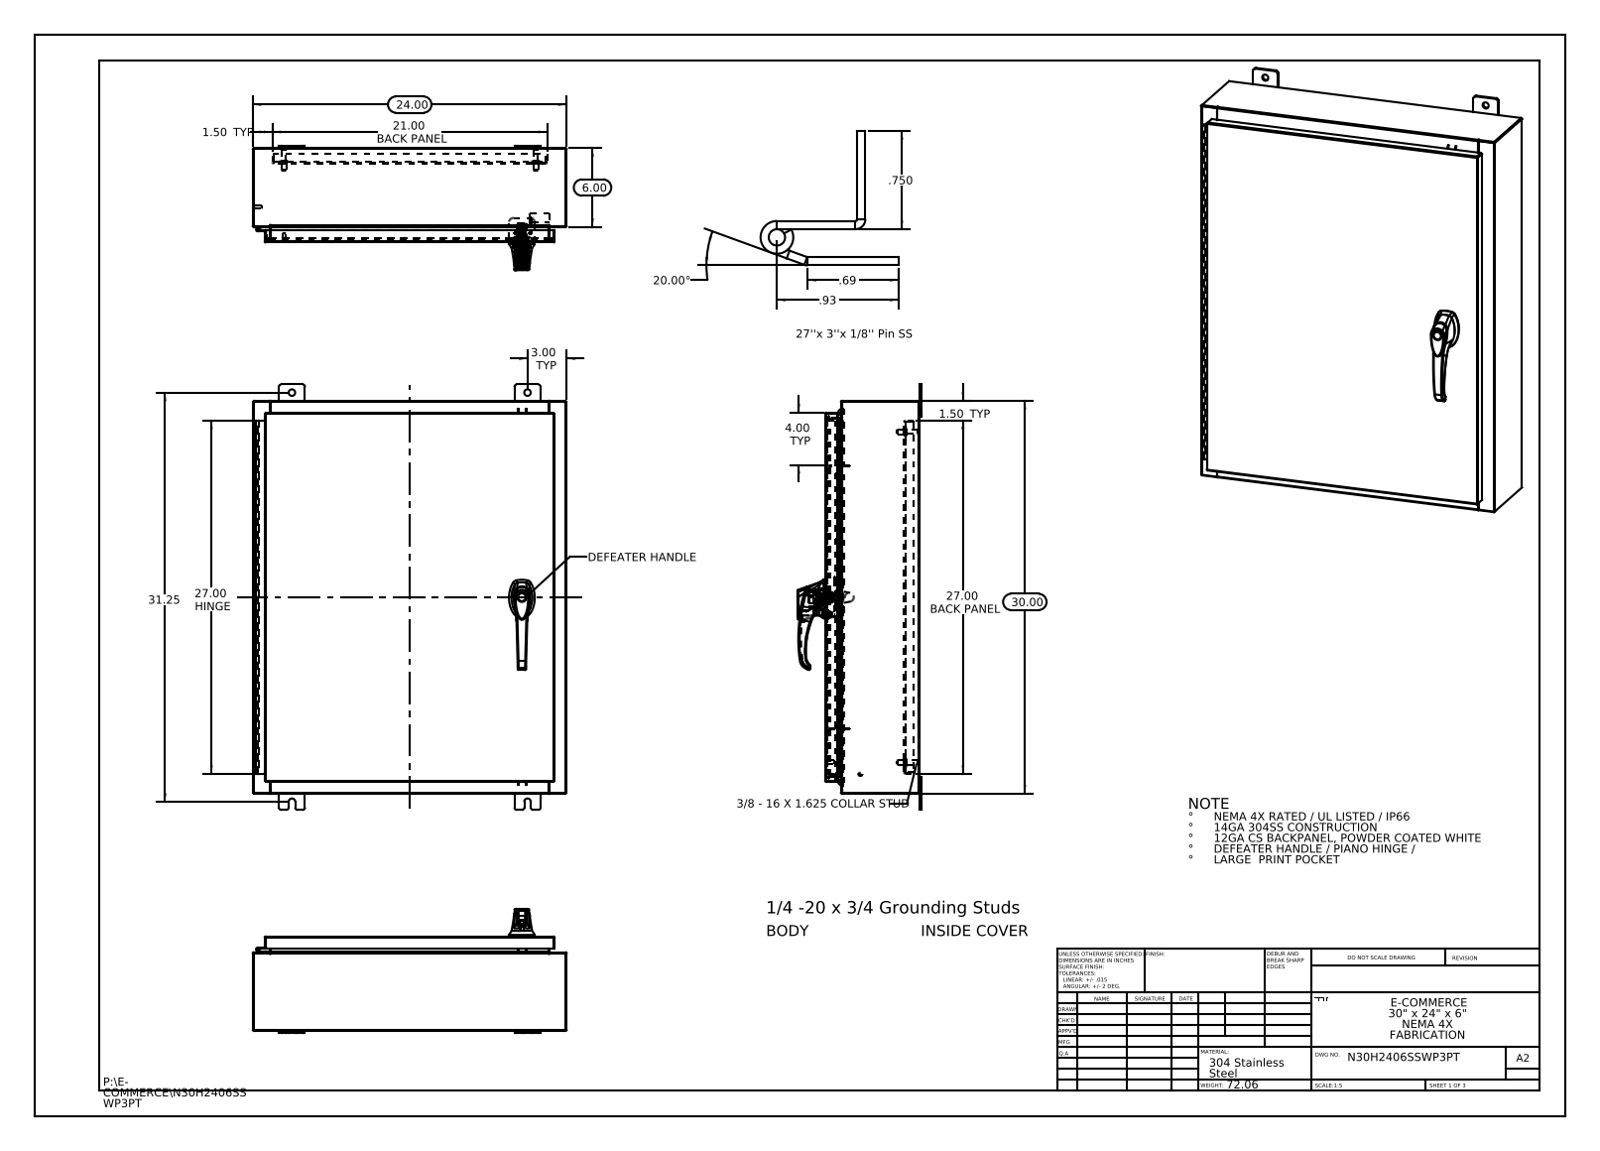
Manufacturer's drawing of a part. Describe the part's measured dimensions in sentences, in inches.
The part is named "297025; N30H2406SSWP3PT Hinge Cover Side; N30H2406SSWP3PT Mounting Studs; N30H2406SSWP3PT (+8 more)". Its 3-D file was written by "SolidWorks 2013 (CONFIG_CONTROL_DESIGN)". It is 37 solids with 2662 faces: 971 planar, 993 cylindrical and 698 other. Overall it measures 32.5 by 24 by 9.495 inches. Its volume is 256.1 cubic inches and its surface area 6 284 square inches. Round holes: 8 of diameter 0.5, 4 of diameter 0.25, 3 of diameter 0.138, 3 of diameter 0.161, 2 of diameter 0.079, 2 of diameter 0.203, 2 of diameter 0.313, 2 of diameter 0.437, 1 of diameter 0.125, 1 of diameter 0.125, 1 of diameter 0.197, 1 of diameter 0.276. Round bosses or shafts: 4 of diameter 0.625, 4 of diameter 0.375, 4 of diameter 0.33, 4 of diameter 0.157, 4 of diameter 0.14, 3 of diameter 0.315, 3 of diameter 0.236, 1 of diameter 1.181. Partial cylindrical surfaces (rounded edges, fillets, slot ends): 37 of radius 0.118, 33 of radius 0.006, 24 of radius 0.013, 24 of radius 0.19, 18 of radius 0.088, 15 of radius 0.039, 12 of radius 0.028, 6 of radius 0.008. The main face-to-face distances are 0.075, 7.126, 0.104, 7.051, 7.201, 1, 1.075, 6.051, 6.126, 1.179. The hole center spacings are 8.369, 0.295, 0.625, 0.841, 1.25, 1.313, 1.561, 1.858.
